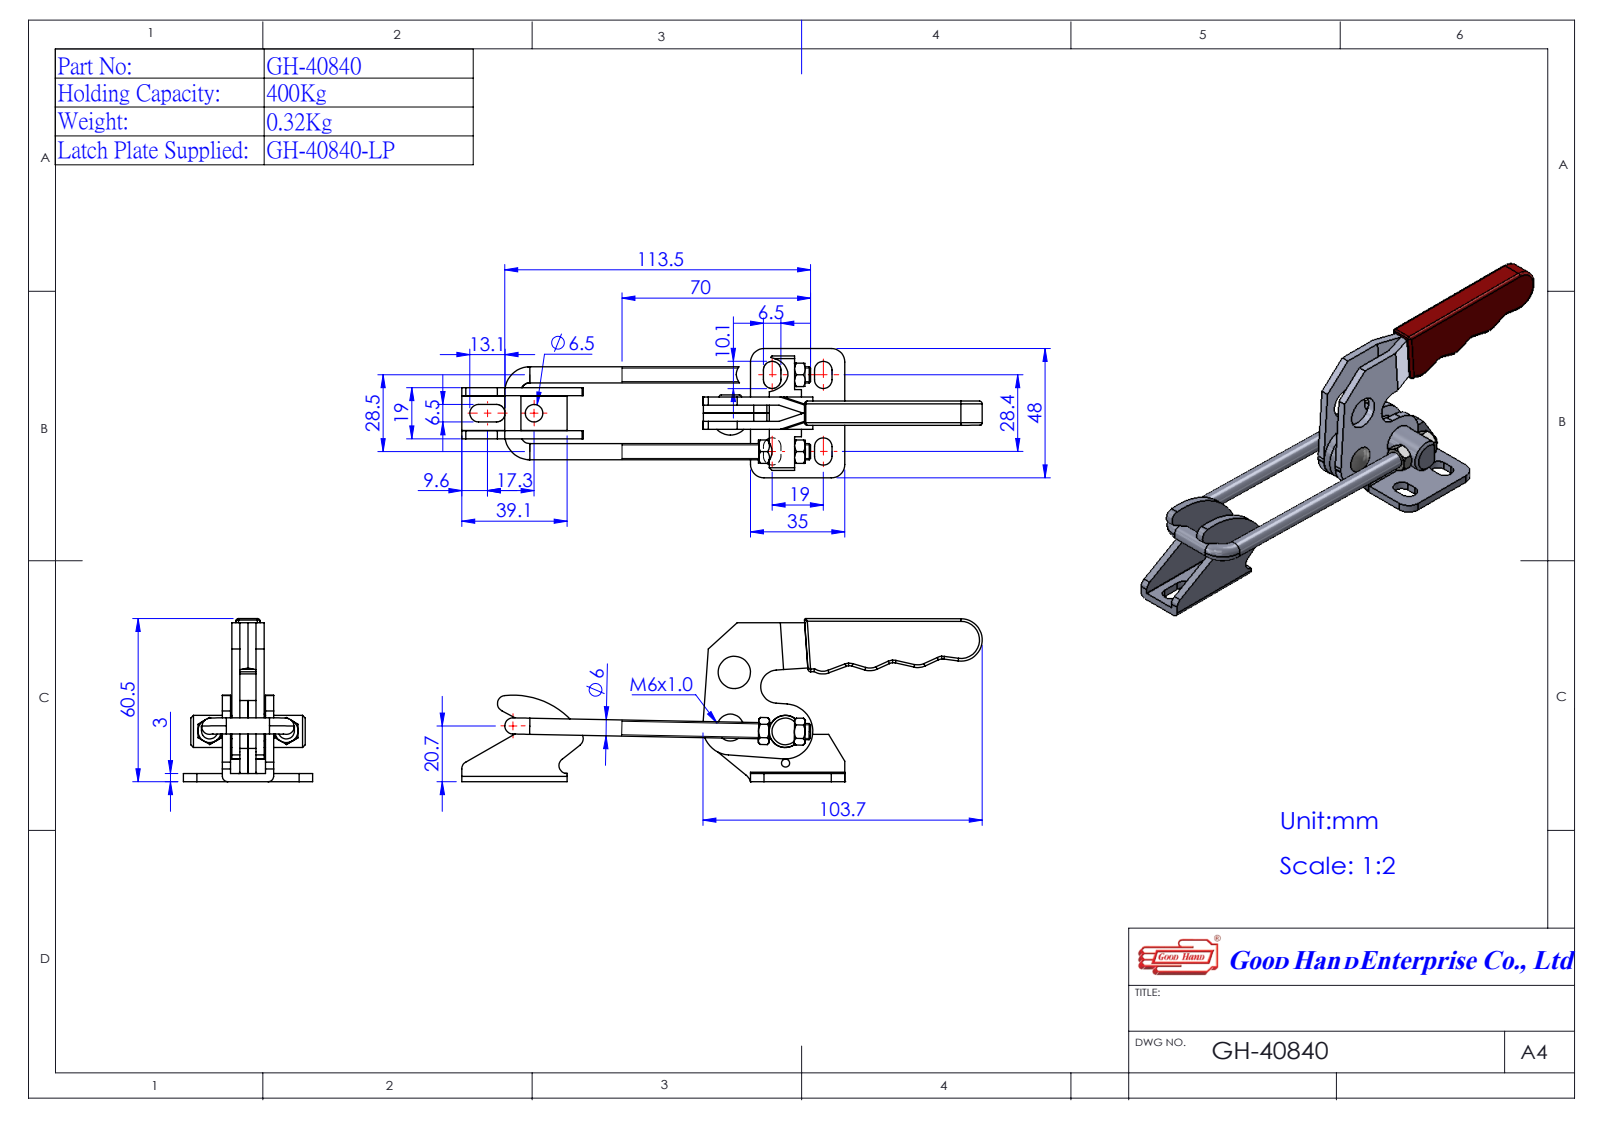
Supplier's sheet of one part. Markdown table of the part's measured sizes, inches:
| quantity | value |
| --- | --- |
| part name | Group2^GH-40840(簡化); Group3^GH-40840(簡化); 14084044-1^GH-40840(簡化); 14084014-1^GH-40840(簡化) (+2 more) |
| STEP written by | SolidWorks 2016 (AUTOMOTIVE_DESIGN) |
| units | inches |
| bodies | 5 solids, 261 faces (126 planar, 102 cylindrical, 33 other) |
| overall size | 7.519 × 2.383 × 1.89 |
| volume | 2.767 in³ |
| surface area | 45.29 in² |
| round holes (diameter × count) | 0.236 × 3, 0.472 × 2, 0.098 × 1, 0.197 × 1, 0.256 × 1 |
| round bosses / shafts (diameter × count) | 0.236 × 2, 0.118 × 1 |
| partial cylindrical surfaces (radius × count) | 0.128 × 10, 0.118 × 4, 0.197 × 4, 0.138 × 2, 0.256 × 2, 0.402 × 2, 0.02 × 1, 0.039 × 1 |
| main face-to-face distances | 0.118, 0.059, 0.354, 0.492, 0.138, 0.413, 0.295, 0.236, 0.256, 0.197 |
| hole center spacings | 0.463, 0.805, 0.807, 0.96, 1.122, 1.14, 1.522, 3.091 |
